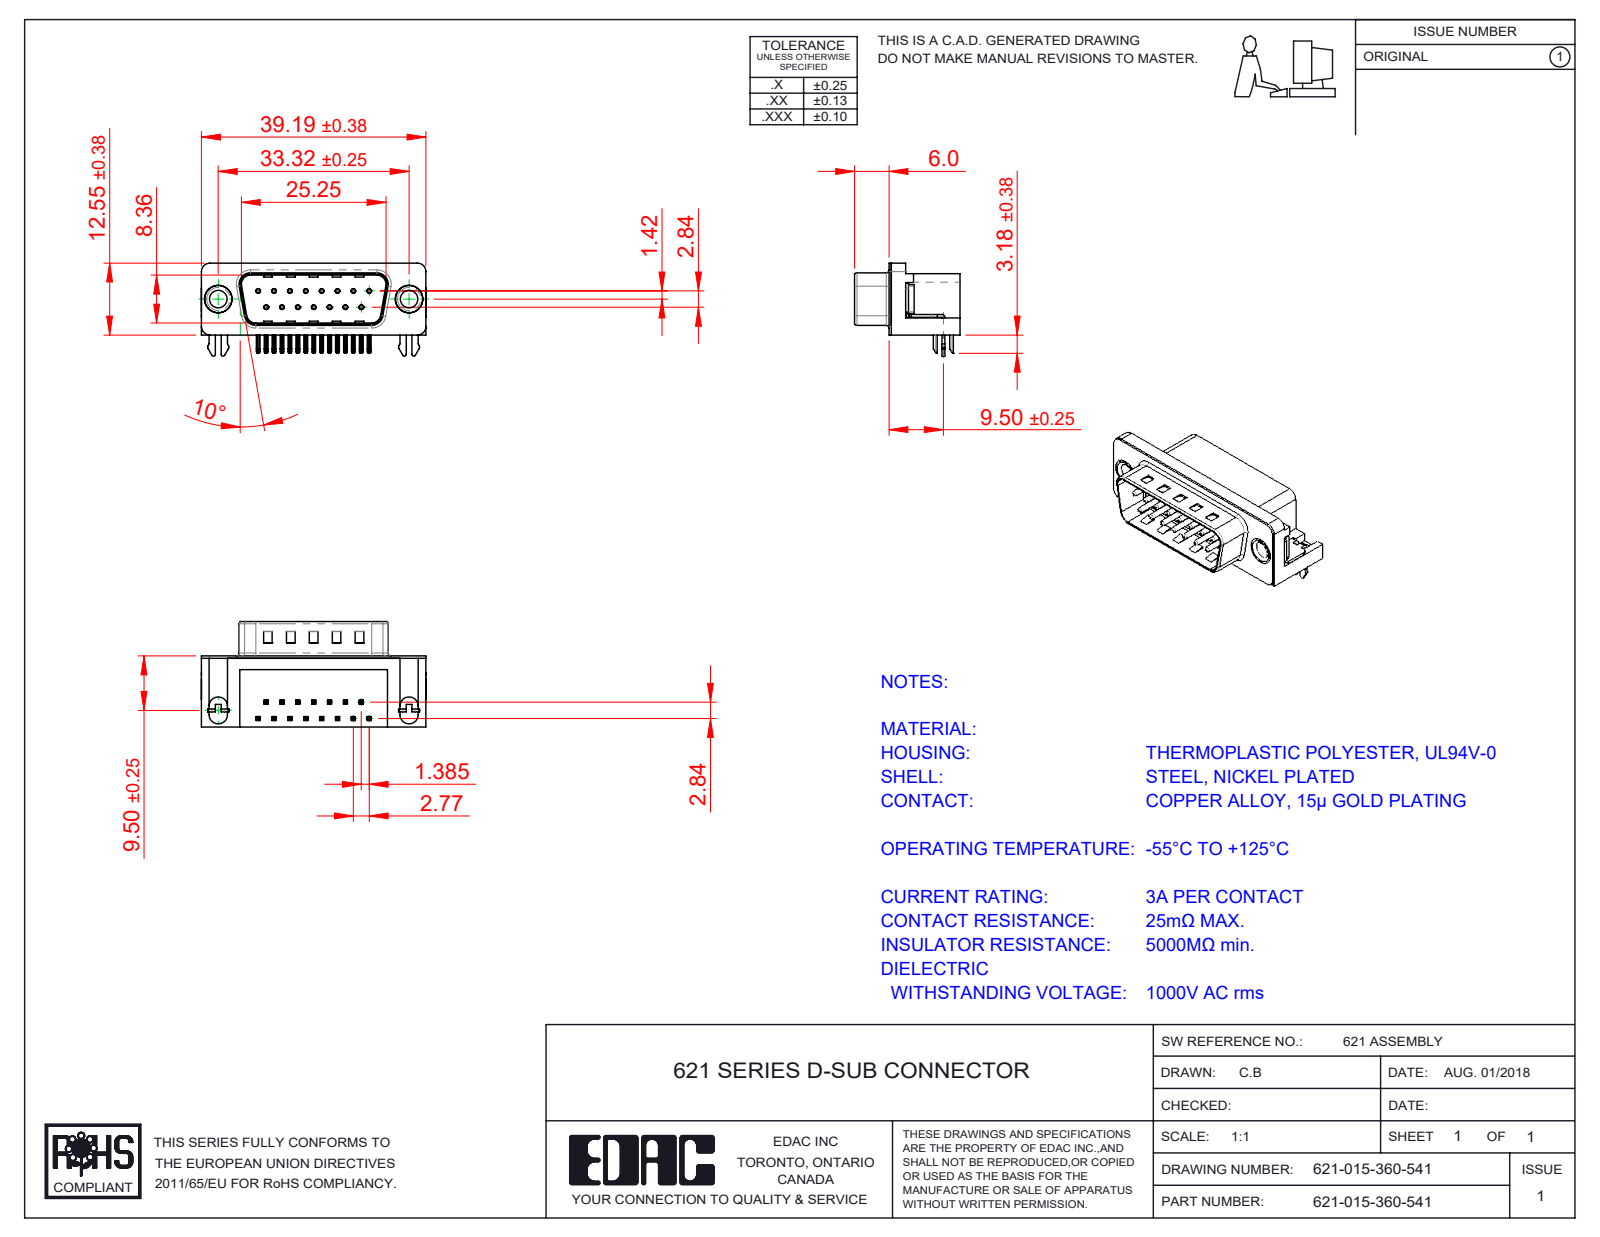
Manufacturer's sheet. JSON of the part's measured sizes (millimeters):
{"part_name": "621 Thru Hole Rivet; 621 Housing_15 Socket; 621 Shell_15 Socket; 621 Contact Top (+3 more)", "step_written_by": "SolidWorks 2016 (CONFIG_CONTROL_DESIGN)", "units": "millimeters", "bodies": {"solids": 21, "faces": 1557, "planar": 935, "cylindrical": 433, "other": 189}, "overall_size": [39.22, 18.4, 16.25], "volume_mm3": 4412, "surface_area_mm2": 5701, "round_holes": [[0.35, 15], [0.8, 15], [2, 2], [3.05, 2], [4, 2], [4.8, 2], [5, 2]], "round_bosses_or_shafts": [[0.75, 15], [4.9, 2], [4.75, 2], [3.85, 2], [3, 2]], "partial_cylinders_radius": [[0.25, 72], [0.12, 30], [1, 16], [0.5, 9], [1.6, 8], [1.5, 6], [0.9, 4], [2, 4]], "face_to_face_distances": [0.4, 12, 10.35, 2.1, 12.4, 10.46, 1.7, 10.86, 8.76, 2.9], "hole_center_spacings": [3.16, 2.77, 5.54, 8.31, 11.08, 5.03, 5.04, 7.48]}
